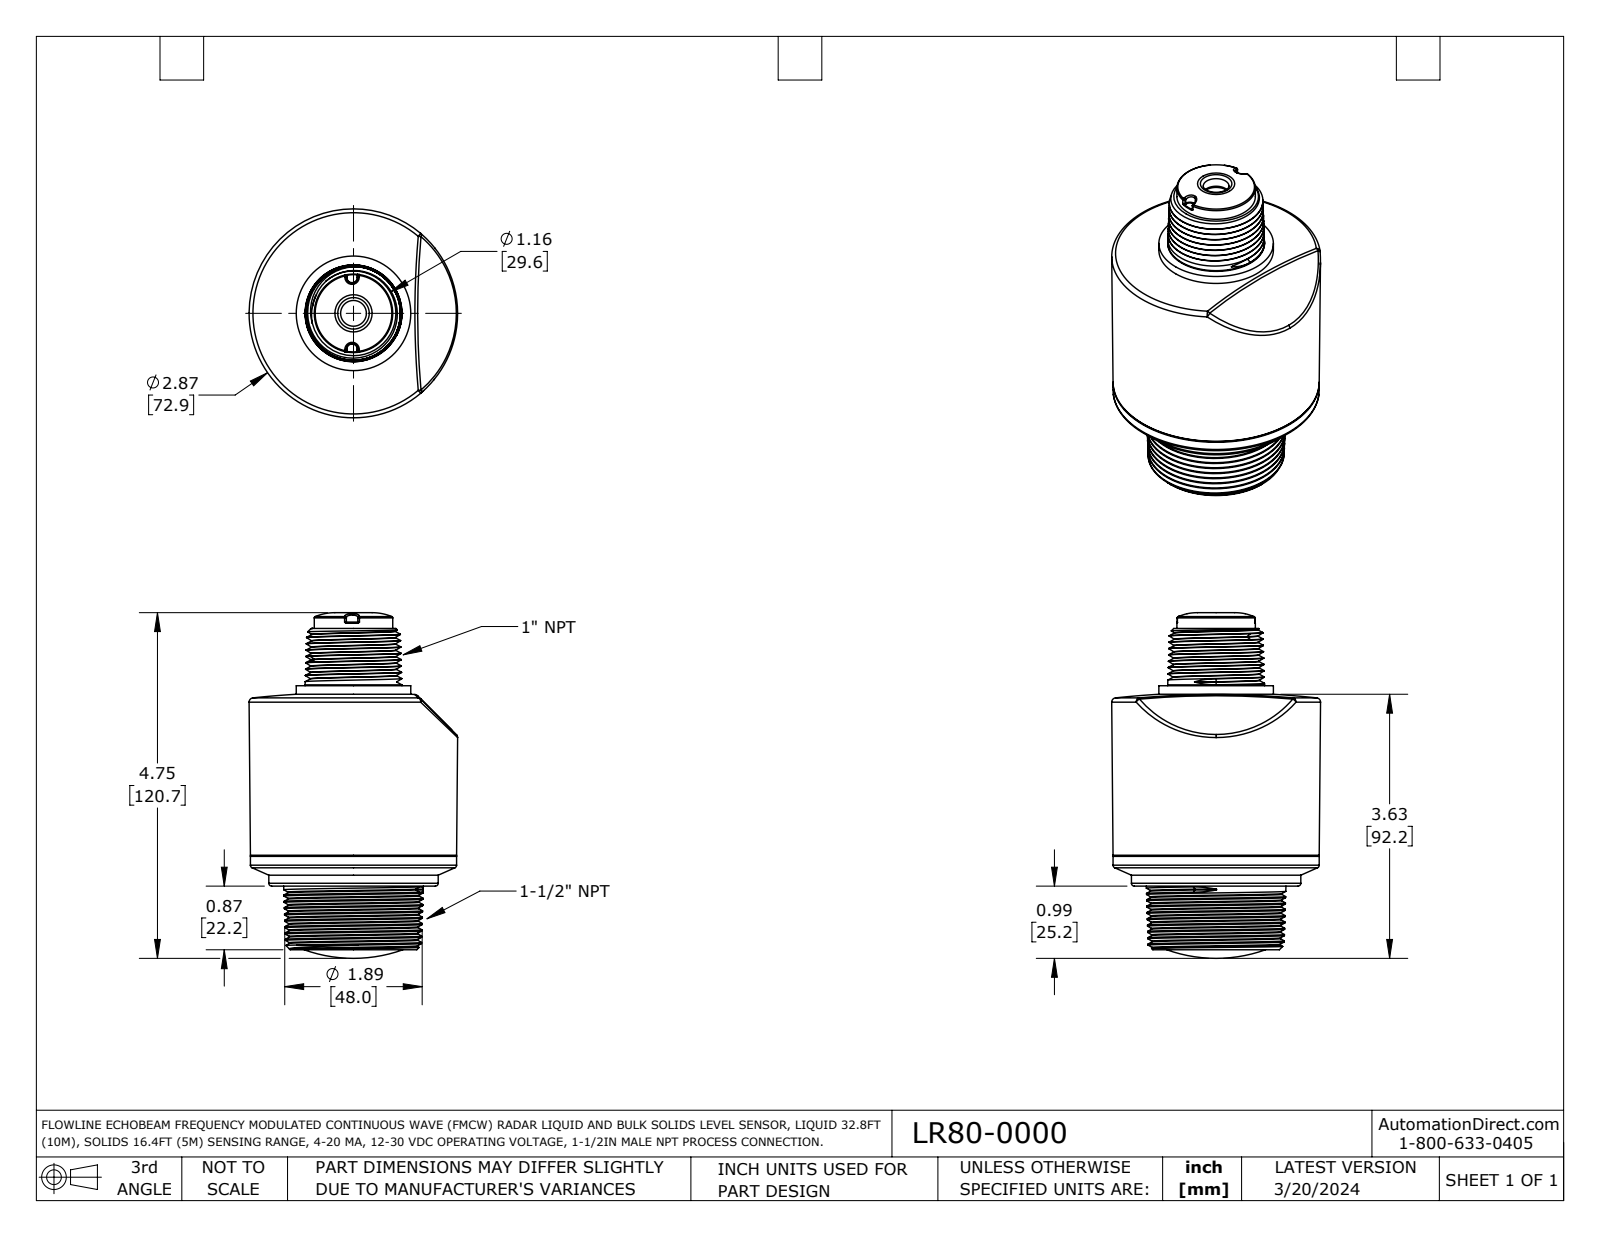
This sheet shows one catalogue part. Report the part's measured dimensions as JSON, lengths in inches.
{"part_name": "LR80-0000", "step_written_by": "SolidWorks 2021 (AUTOMOTIVE_DESIGN)", "units": "inches", "bodies": {"solids": 3, "faces": 366, "planar": 142, "cylindrical": 44, "other": 180}, "overall_size": [4.751, 2.871, 2.867], "volume_in3": 5.49, "surface_area_in2": 89.45, "round_holes": [[0.354, 1], [0.661, 1], [0.807, 1], [1.524, 1], [2.196, 1], [2.248, 1], [2.402, 1], [2.698, 1]], "round_bosses_or_shafts": [[2.835, 1], [2.329, 1], [1.575, 1], [1.331, 1], [1.079, 1], [0.866, 1], [0.795, 1]], "partial_cylinders_radius": [[0.02, 4], [0.008, 2], [0.079, 2], [0.252, 1]], "face_to_face_distances": [0.317, 0.821, 1.138, 3.219, 2.398, 2.081, 2.719, 1.898, 1.581, 0.5]}
